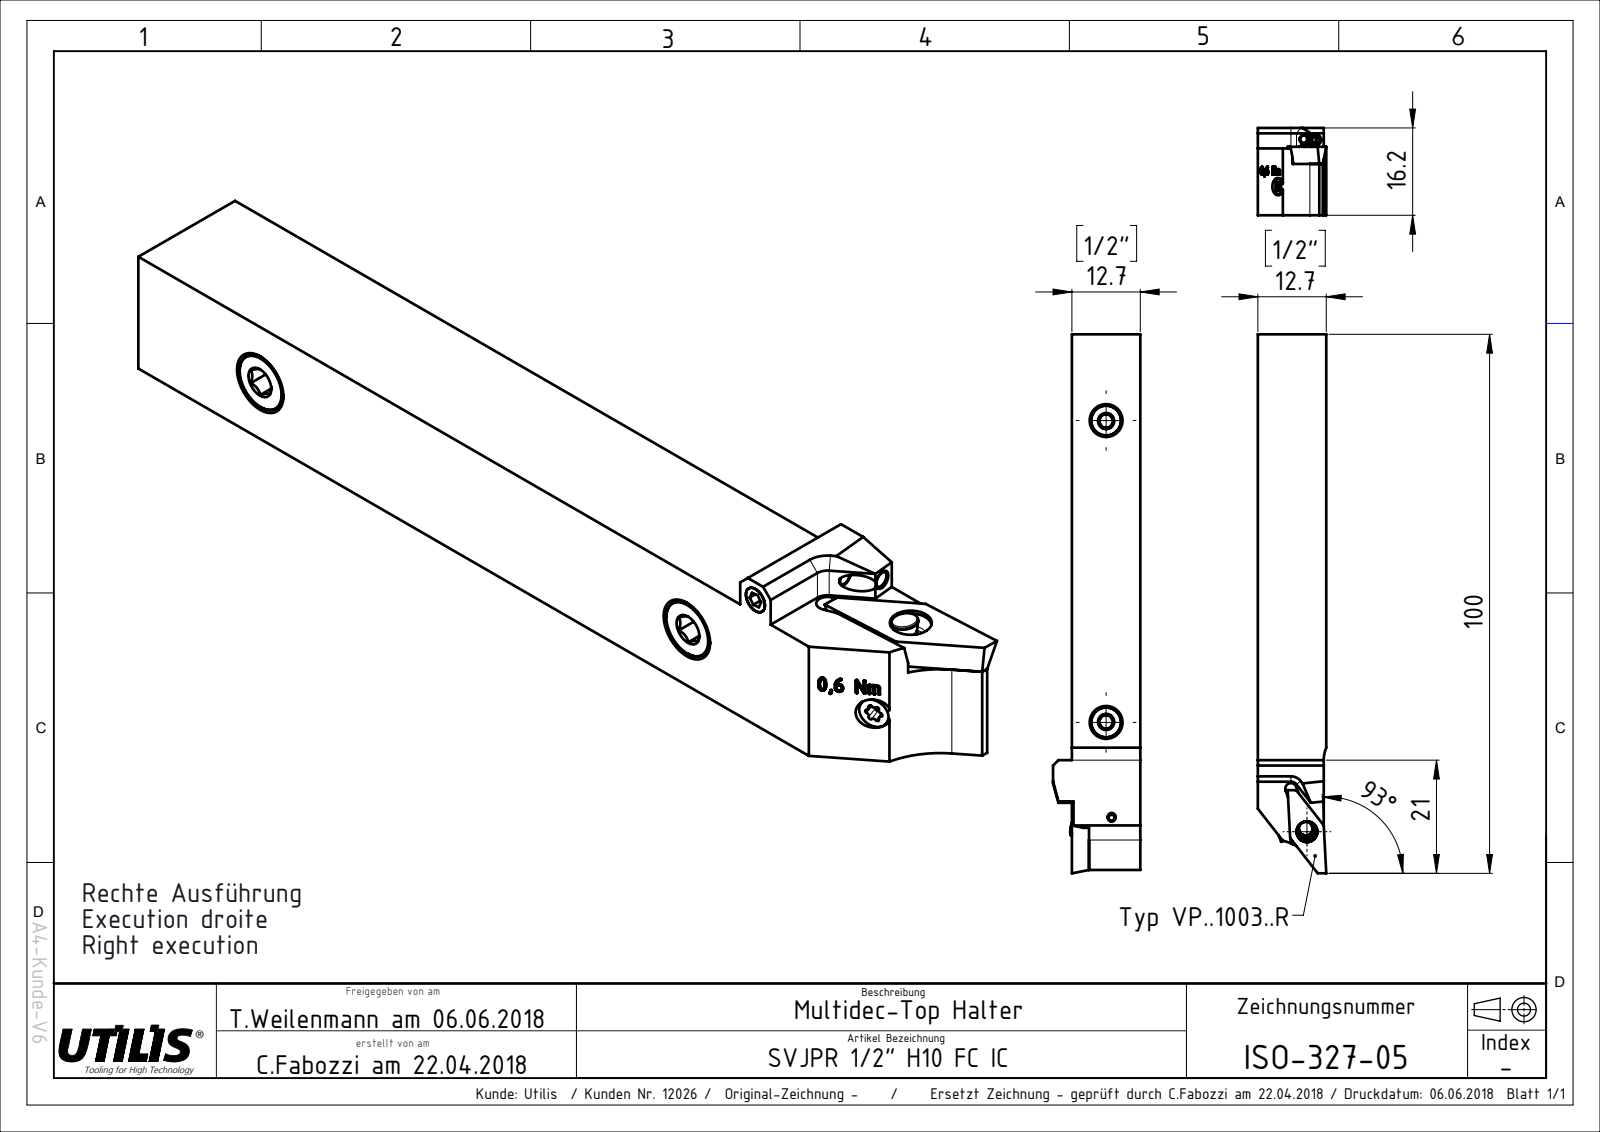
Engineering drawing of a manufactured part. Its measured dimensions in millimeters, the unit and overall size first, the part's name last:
Units: millimetres
Overall size (bounding box): 100 × 16.2 × 12.7
Round holes (diameter × count): ⌀3.2 ×1
Partial cylindrical surfaces — rounded edges, fillets, slot ends (radius × count): R1.05 ×1, R1.31 ×1, R6 ×1, R6.1 ×1, R8.81 ×1
Main face-to-face distances: 12.7, 12.23, 0.47, 12.4, 79, 16.2, 3.8, 3.5, 2, 4
Volume: 15 254 mm³ · Surface area: 5 345 mm²
Bodies: 1 solid, 124 faces (63 planar, 8 cylindrical, 53 other)
Part name (STEP PRODUCT): ISO-327-05
STEP written by: SolidWorks 2017 (AUTOMOTIVE_DESIGN)
